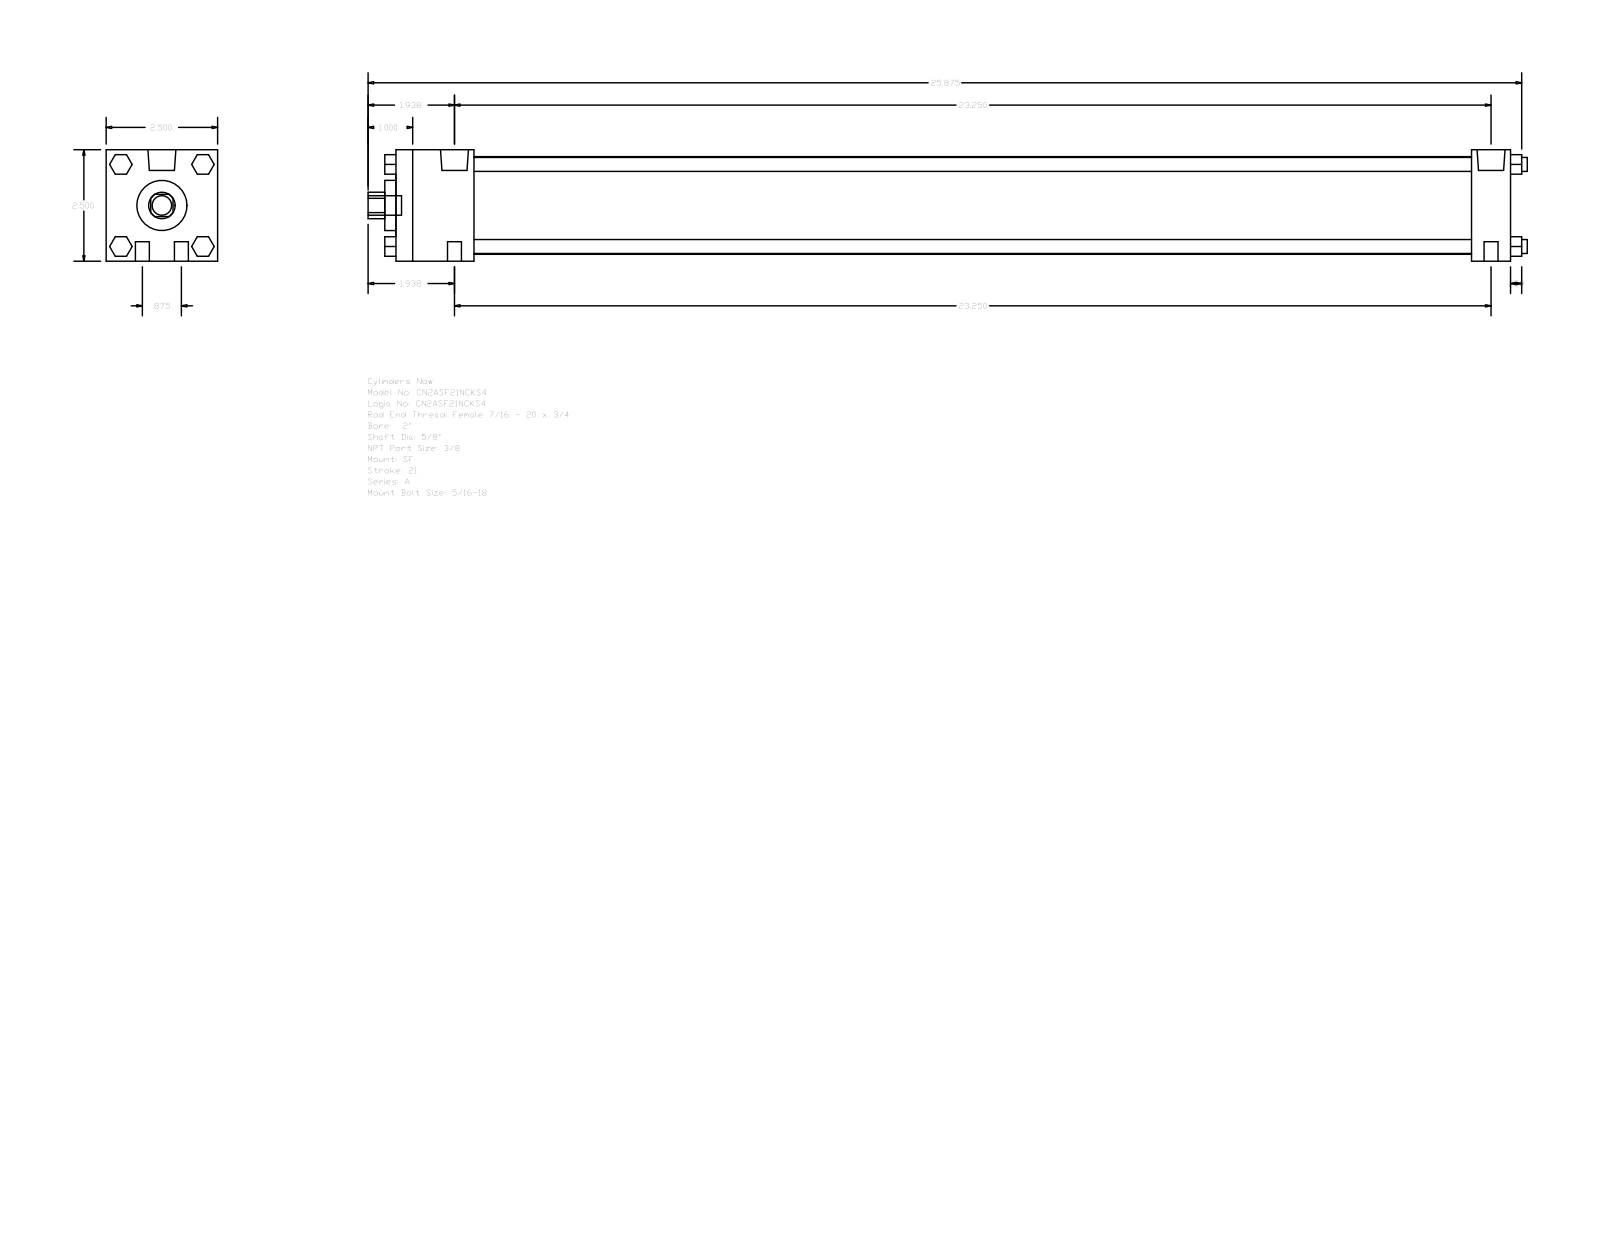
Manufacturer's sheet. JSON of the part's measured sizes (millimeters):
{"part_name": "A_SF__0200_0.625", "step_written_by": "GSSL Pune (CONFIG_CONTROL_DESIGN)", "units": "millimeters", "bodies": {"solids": 0, "faces": 124, "planar": 94, "cylindrical": 30, "other": 0}, "overall_size": [660.4, 63.5, 63.5], "round_holes": [[15.88, 1], [28.57, 1], [55.63, 1]], "round_bosses_or_shafts": [[7.94, 8], [15.93, 2], [5.56, 2], [11.11, 1]], "partial_cylinders_radius": [[7.54, 1]], "face_to_face_distances": [63.5, 635, 612.77, 22.23, 44.45, 568.32, 590.55, 641.35, 6.35, 50.8]}
